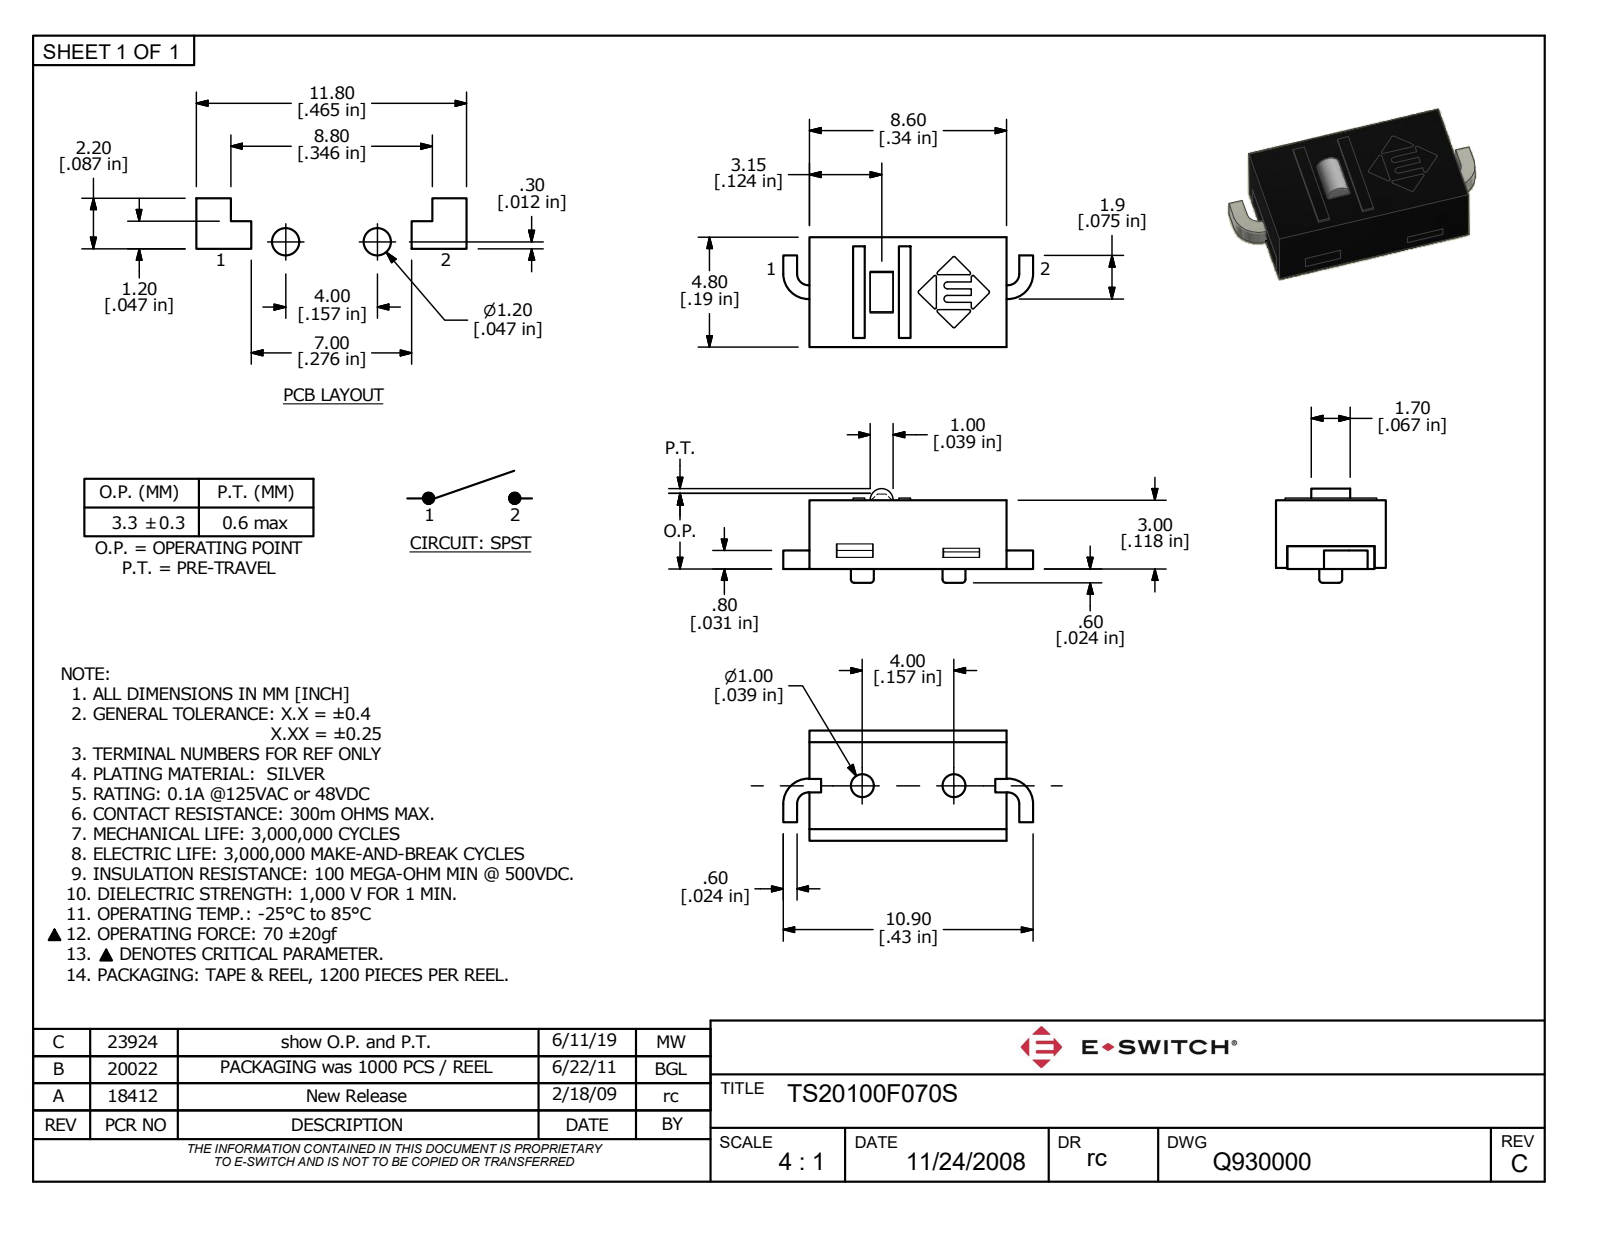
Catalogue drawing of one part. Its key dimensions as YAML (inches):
part_name: "TS20100F070S"
step_written_by: "Autodesk Inventor 2012 (CONFIG_CONTROL_DESIGN)"
units: inches
bodies: {solids: 1, faces: 150, planar: 126, cylindrical: 22, other: 2}
overall_size: [0.429, 0.189, 0.161]
volume: 0.005
surface_area: 0.454
round_bosses_or_shafts:
  - {diameter: 0.039, count: 2}
partial_cylinders:
  - {radius: 0.02, count: 4}
  - {radius: 0.006, count: 2}
  - {radius: 0.043, count: 2}
face_to_face_distances: [0.02, 0.118, 0.016, 0.102, 0.079, 0.169, 0.189, 0.063, 0.039, 0.075]
